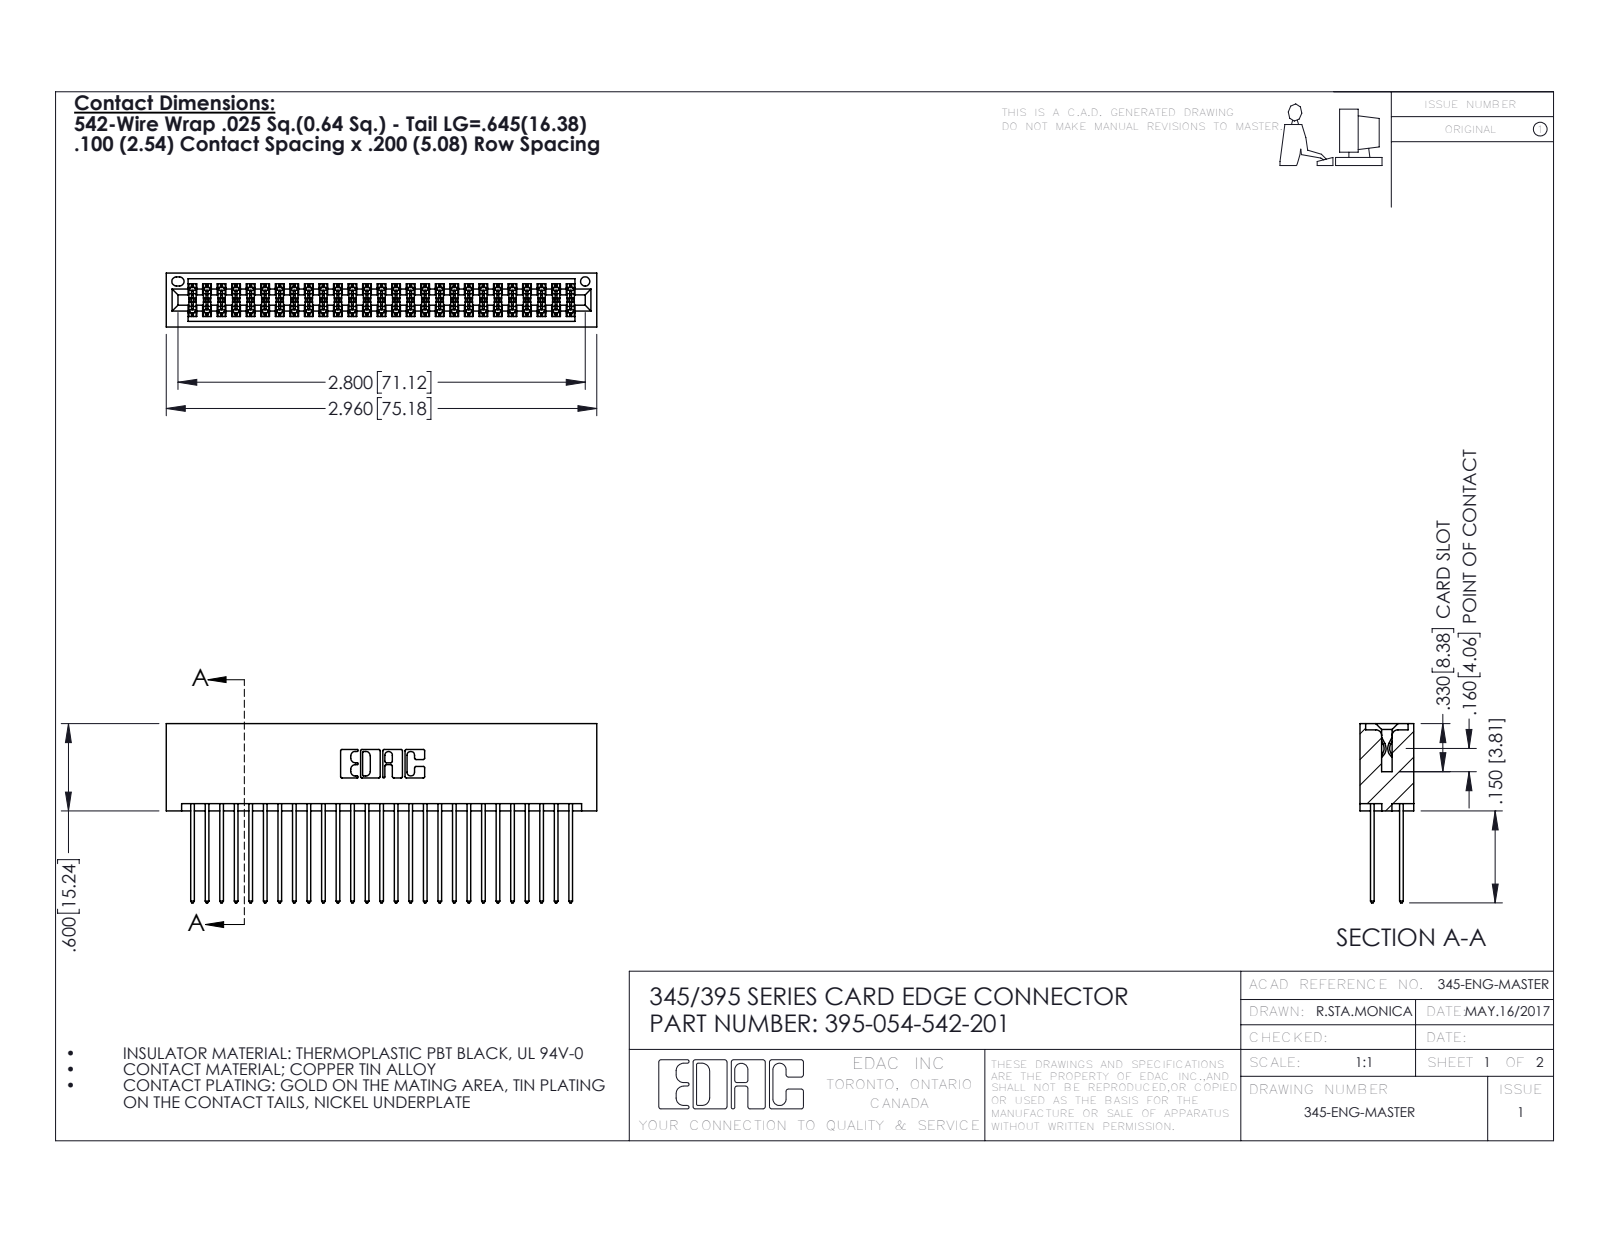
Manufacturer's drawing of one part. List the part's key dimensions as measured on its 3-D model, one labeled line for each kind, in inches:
Part name (STEP PRODUCT): 395-054-542-201; 345-292-001_345-293-142; 345 Part_No Mounting Lugs
STEP written by: SolidWorks 2016 (CONFIG_CONTROL_DESIGN)
Units: inches
Bodies: 55 solids, 2818 faces (1858 planar, 960 cylindrical, 0 other)
Overall size (bounding box): 2.96 × 1.232 × 0.37
Volume: 0.49 in³ · Surface area: 20.25 in²
Round holes (diameter × count): ⌀0.064 ×1
Partial cylindrical surfaces — rounded edges, fillets, slot ends (radius × count): R0.006 ×81, R0.01 ×54, R0.01 ×22, R0.007 ×6, R0.031 ×6, R0.026 ×3, R0.014 ×2, R0.019 ×2
Main face-to-face distances: 0.298, 0.072, 0.2, 0.098, 0.272, 0.025, 0.225, 0.37, 0.175, 0.149
